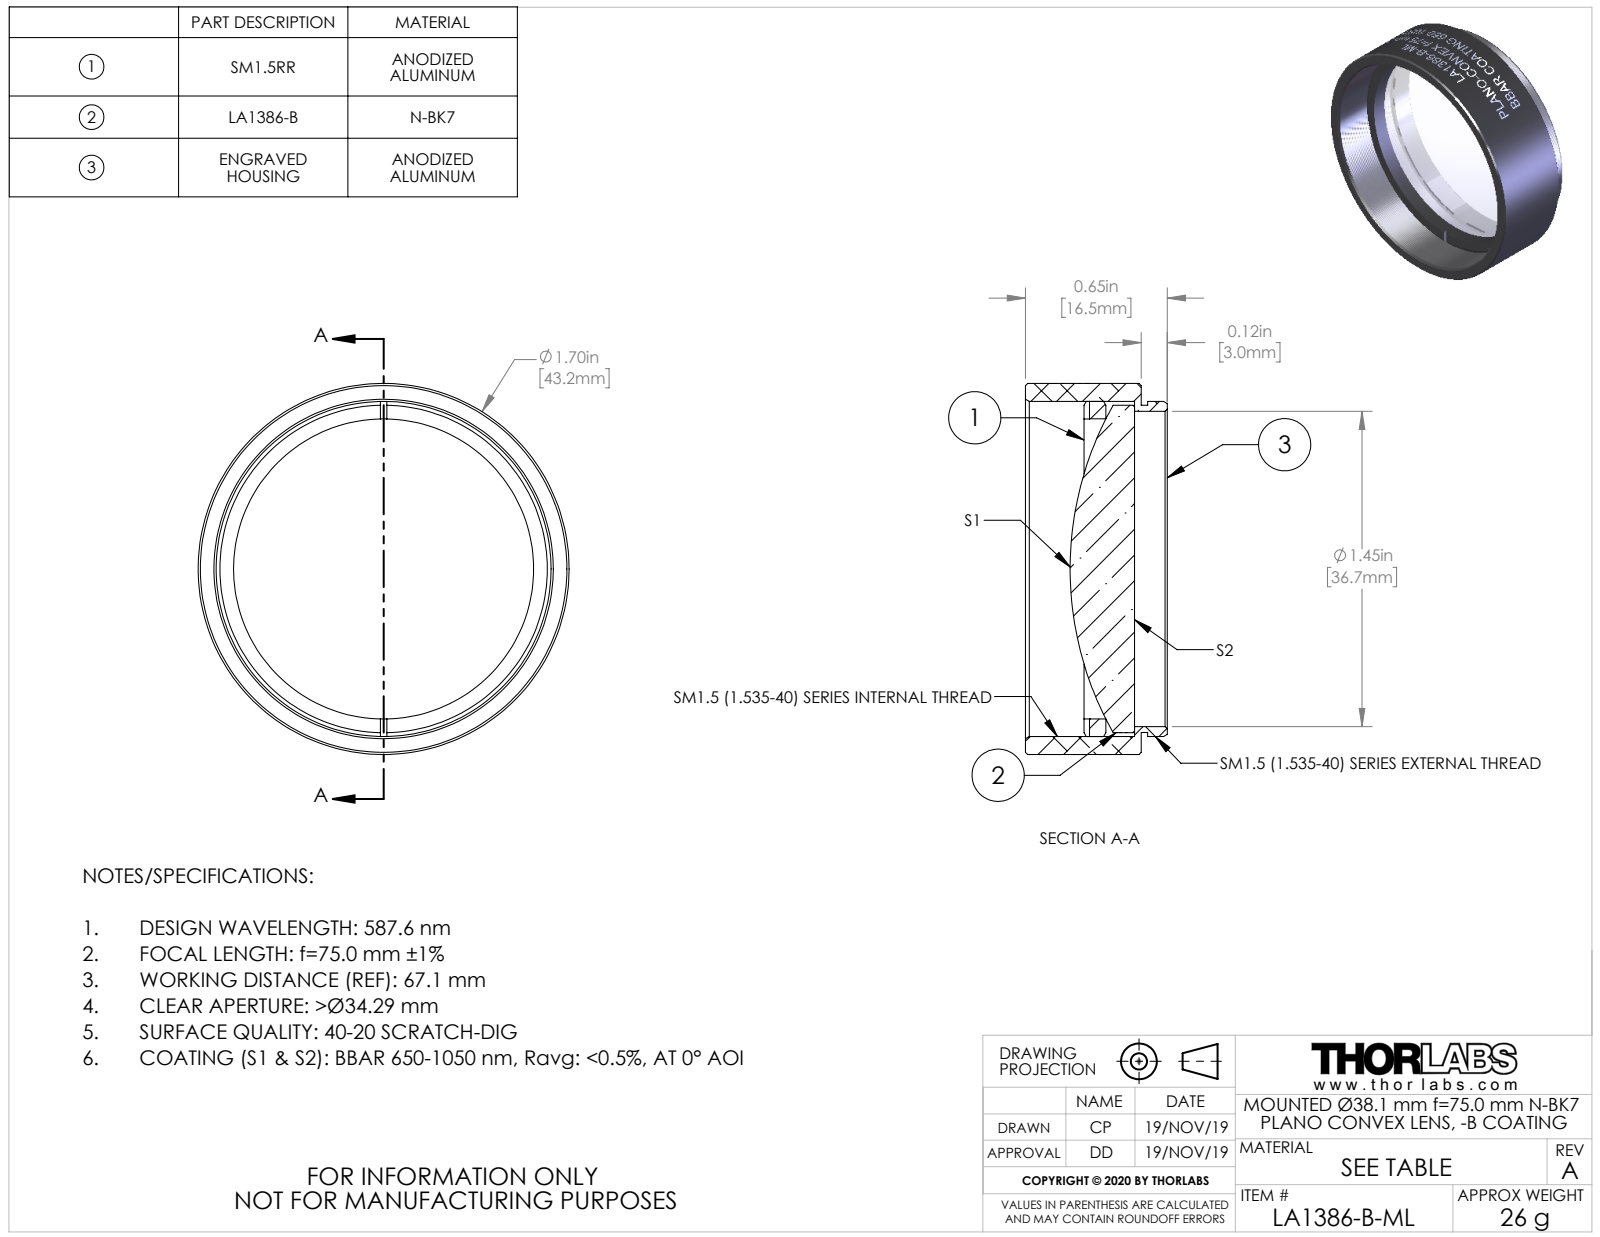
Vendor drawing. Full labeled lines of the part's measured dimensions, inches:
Part name (STEP PRODUCT): TTN200732-E0W
STEP written by: SolidWorks 2018 (CONFIG_CONTROL_DESIGN)
Units: inches
Bodies: 3 solids, 160 faces (15 planar, 126 cylindrical, 19 other)
Overall size (bounding box): 1.7 × 1.7 × 0.65
Volume: 0.637 in³ · Surface area: 13.45 in²
Round holes (diameter × count): ⌀1.375 ×1, ⌀1.445 ×1
Round bosses / shafts (diameter × count): ⌀1.7 ×1, ⌀1.535 ×1, ⌀1.5 ×1, ⌀1.499 ×1
Main face-to-face distances: 0.03, 0.53, 0.5, 0.162, 0.132, 0.368, 0.262, 0.232, 0.1, 0.268
